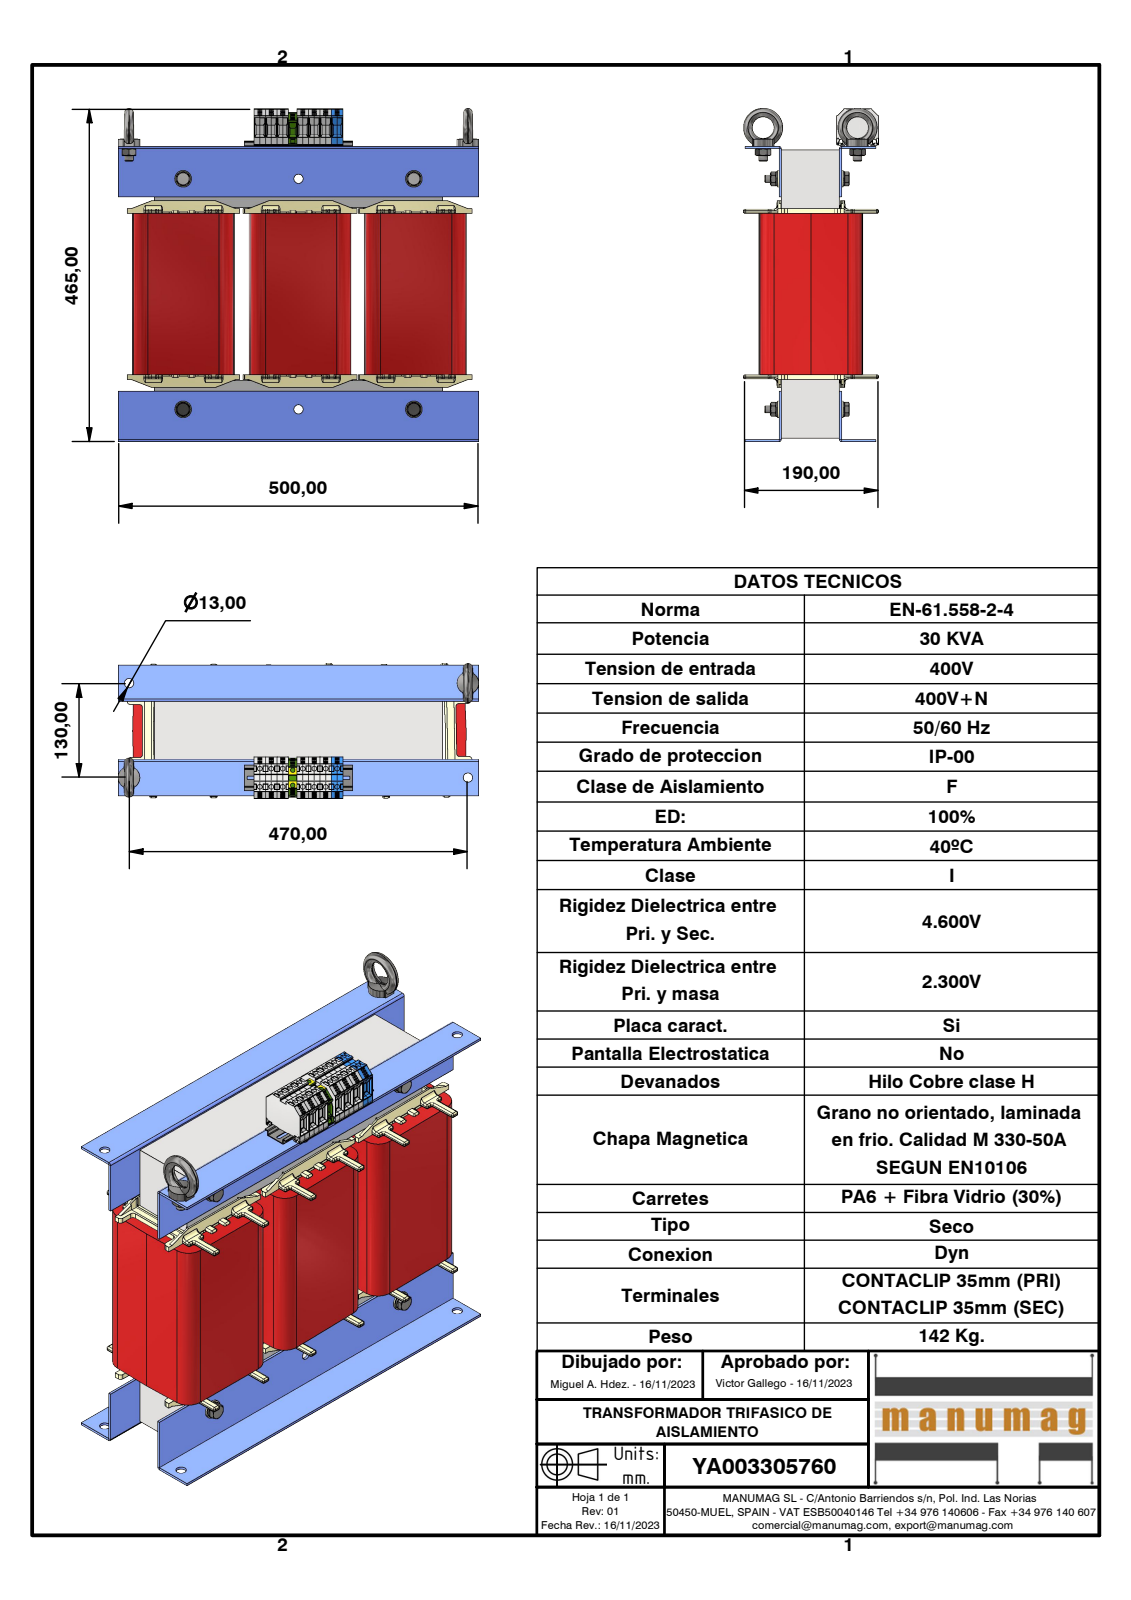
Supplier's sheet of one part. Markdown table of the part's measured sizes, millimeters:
| quantity | value |
| --- | --- |
| part name | YA003305760; 3UI240 400 x 400 - 80; RC80 NT080; centrador M10 (+8 more) |
| STEP written by | Autodesk Inventor 2023 (AUTOMOTIVE_DESIGN) |
| units | millimeters |
| bodies | 45 solids, 8809 faces (4833 planar, 2622 cylindrical, 1354 other) |
| overall size | 500 × 463 × 186.38 |
| volume | 18 910 000 mm³ |
| surface area | 2 376 000 mm² |
| round holes (diameter × count) | 6.5 × 14, 13 × 10, 15 × 6, 2 × 4, 8.38 × 4, 10 × 4, 10.5 × 4, 6.3 × 2, 10.11 × 2, 30 × 2 |
| round bosses / shafts (diameter × count) | 0.6 × 12, 23 × 4, 20 × 4, 15.4 × 4, 11.5 × 4, 9.19 × 4, 54 × 2, 12 × 2 |
| partial cylindrical surfaces (radius × count) | 0.3 × 494, 2 × 328, 0.5 × 188, 1 × 102, 1.9 × 60, 5 × 36, 0.25 × 34, 0.81 × 33 |
| main face-to-face distances | 80, 3, 5.8, 83, 1.8, 22.96, 28.76, 407, 24.76, 4 |
| hole center spacings | 15.9, 29.63, 25, 31.8, 40.45, 59.6, 64.63, 75.5 |
